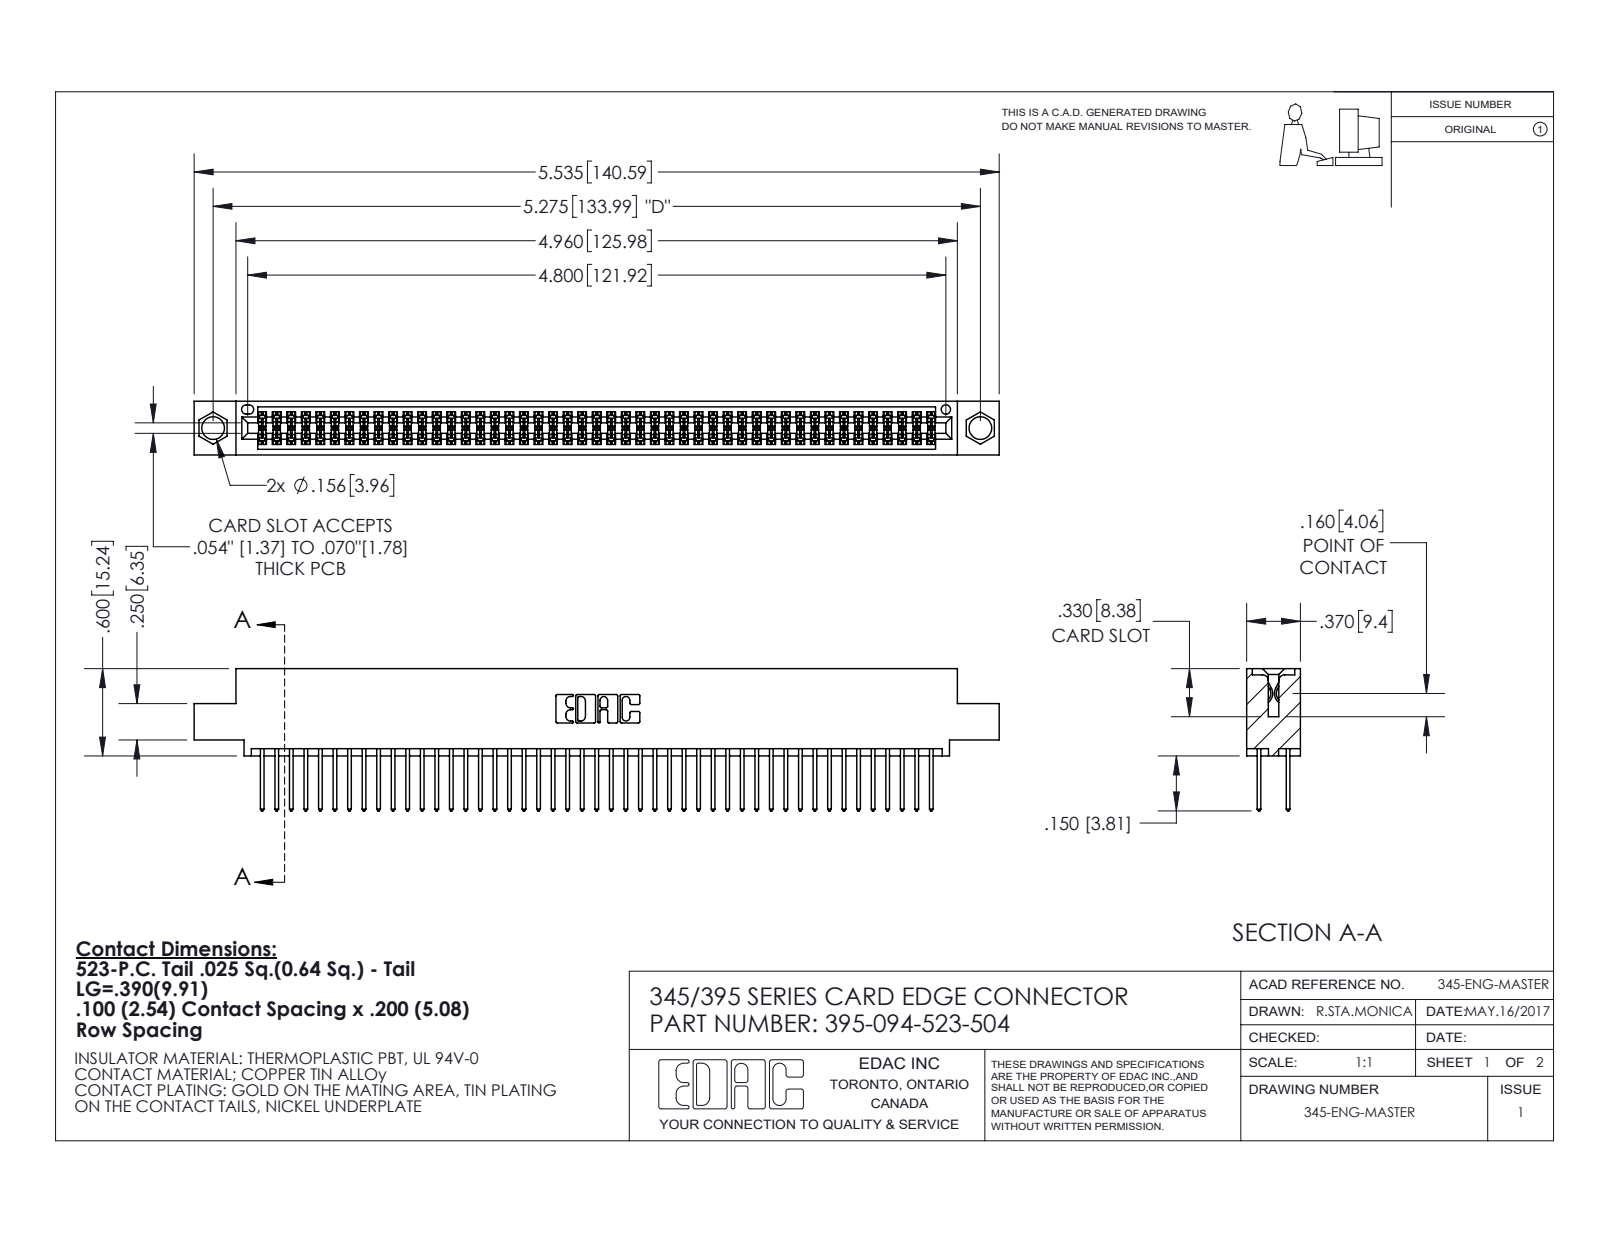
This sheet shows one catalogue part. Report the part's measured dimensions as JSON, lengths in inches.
{"part_name": "345 Part_0.110 Offset - 0.156 Dia-TI; 345-292-001_345-293-123; 395-094-523-504", "step_written_by": "SolidWorks 2020 (CONFIG_CONTROL_DESIGN)", "units": "inches", "bodies": {"solids": 95, "faces": 4844, "planar": 3200, "cylindrical": 1644, "other": 0}, "overall_size": [5.535, 0.977, 0.37], "volume_in3": 0.837, "surface_area_in2": 32.83, "round_holes": [[0.156, 2], [0.064, 1]], "partial_cylinders_radius": [[0.006, 188], [0.01, 94], [0.01, 22], [0.007, 6], [0.031, 6], [0.026, 3], [0.014, 2], [0.019, 2]], "face_to_face_distances": [0.072, 0.298, 0.2, 0.098, 0.272, 0.025, 0.37, 0.225, 0.175, 0.149], "hole_center_spacings": [0.27, 5.039, 5.275]}
